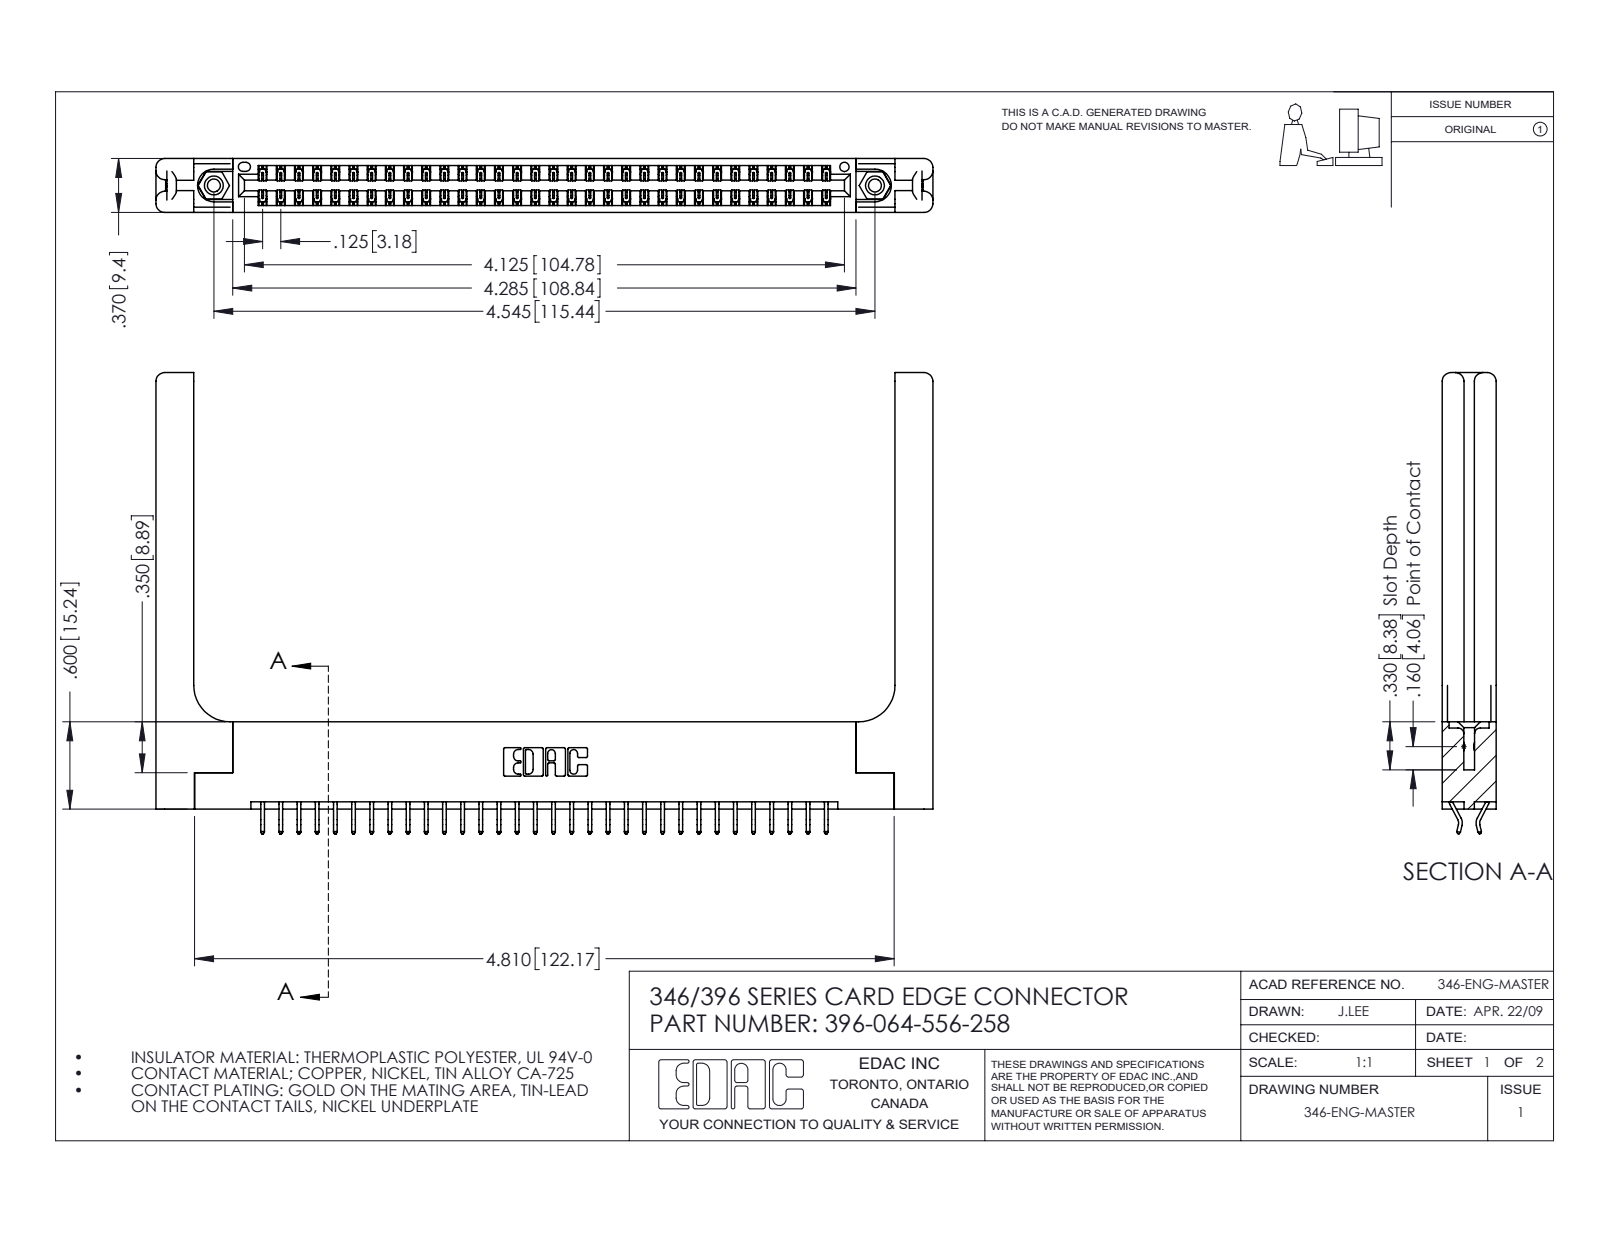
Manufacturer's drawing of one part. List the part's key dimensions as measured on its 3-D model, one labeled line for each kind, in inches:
Part name (STEP PRODUCT): 346-220-058_345-220-058; 345-292-001_556 Tail; 346 Part_Flush Mounting Lugs - 0.156 Dia-TH; 396-064-556-258 (+1 more)
STEP written by: SolidWorks 2016 (CONFIG_CONTROL_DESIGN)
Units: inches
Bodies: 69 solids, 4090 faces (2720 planar, 1310 cylindrical, 60 other)
Overall size (bounding box): 5.341 × 3.17 × 0.37
Volume: 1.26 in³ · Surface area: 35.39 in²
Round holes (diameter × count): ⌀0.089 ×2, ⌀0.125 ×2, ⌀0.156 ×2, ⌀0.064 ×1
Round bosses / shafts (diameter × count): ⌀0.155 ×2
Partial cylindrical surfaces — rounded edges, fillets, slot ends (radius × count): R0.006 ×96, R0.01 ×22, R0.06 ×16, R0.007 ×6, R0.031 ×6, R0.026 ×3, R0.01 ×2, R0.014 ×2
Main face-to-face distances: 0.37, 0.048, 0.322, 0.072, 0.148, 0.15, 0.25, 0.025, 0.298, 0.275
Hole centre spacings: 0.246, 4.337, 4.545
